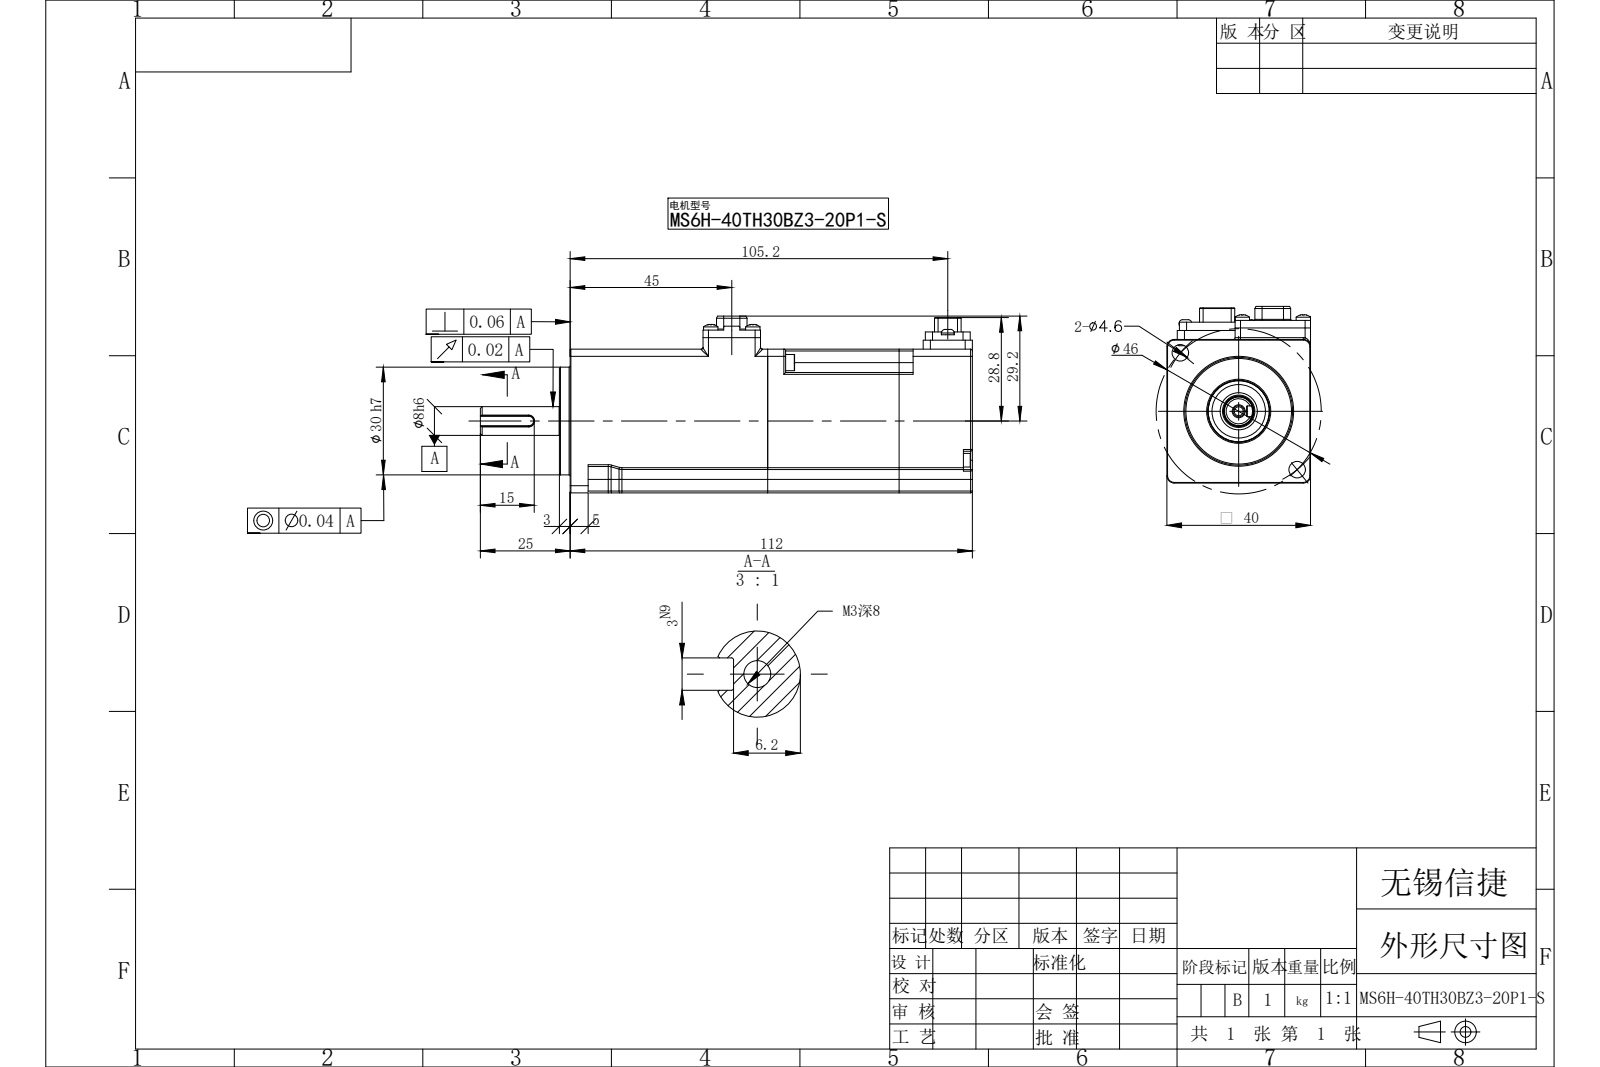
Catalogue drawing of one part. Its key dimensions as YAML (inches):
part_name: "MS6H-40TH30BZ3-20P1-S"
step_written_by: "SolidWorks 2022 (CONFIG_CONTROL_DESIGN)"
units: inches
bodies: {solids: 0, faces: 687, planar: 353, cylindrical: 219, other: 115}
overall_size: [5.394, 1.937, 1.575]
round_holes:
  - {diameter: 0.083, count: 4}
  - {diameter: 0.063, count: 2}
  - {diameter: 0.181, count: 2}
  - {diameter: 0.098, count: 1}
  - {diameter: 0.354, count: 1}
  - {diameter: 0.585, count: 1}
round_bosses_or_shafts:
  - {diameter: 0.157, count: 4}
  - {diameter: 0.15, count: 4}
  - {diameter: 0.177, count: 2}
  - {diameter: 0.138, count: 2}
  - {diameter: 1.181, count: 1}
  - {diameter: 0.669, count: 1}
  - {diameter: 0.407, count: 1}
  - {diameter: 0.335, count: 1}
partial_cylinders:
  - {radius: 0.02, count: 60}
  - {radius: 0.079, count: 16}
  - {radius: 0.008, count: 15}
  - {radius: 0.012, count: 10}
  - {radius: 0.118, count: 8}
  - {radius: 0.059, count: 5}
  - {radius: 0.039, count: 4}
  - {radius: 0.098, count: 4}
face_to_face_distances: [1.575, 0.256, 1.319, 1.063, 4.409, 0.118, 4.528, 0.11, 0.098, 1.673]
hole_center_spacings: [0.315, 0.654, 0.726, 0.906, 0.669, 1.811, 2.211, 2.291]
